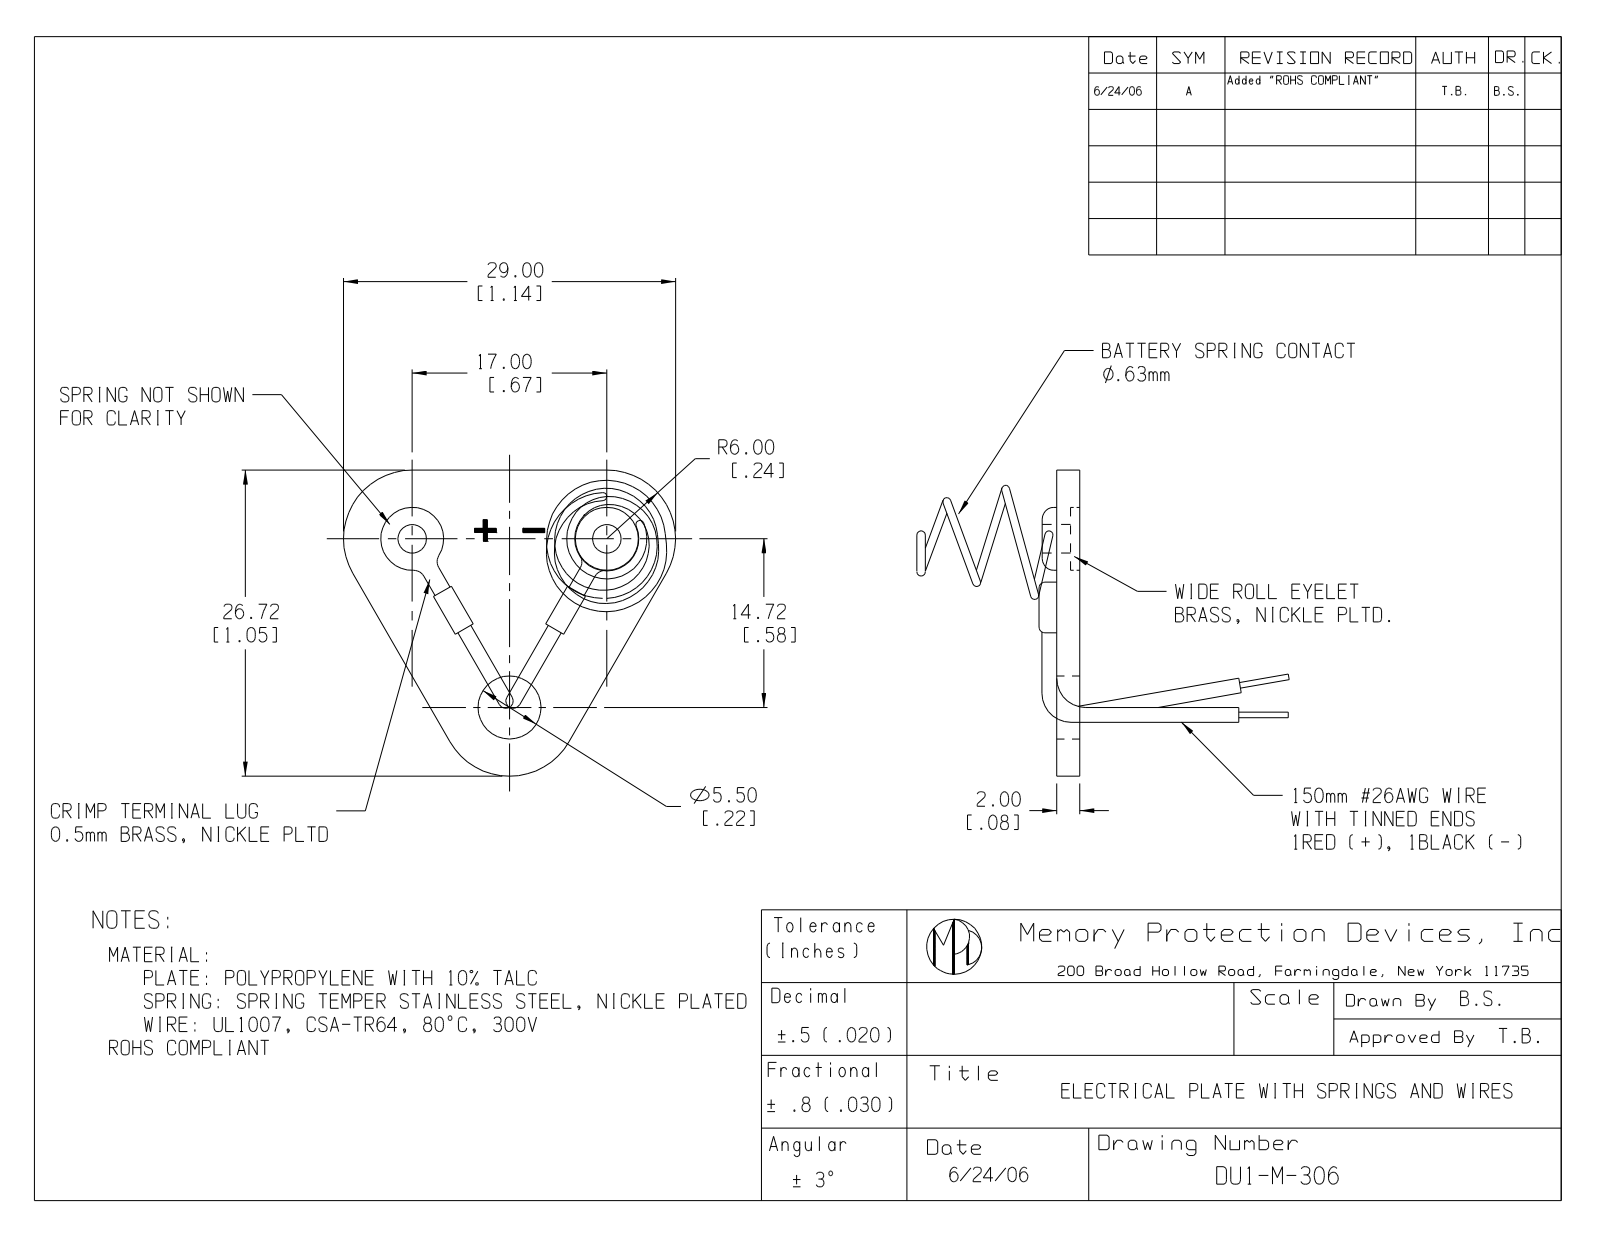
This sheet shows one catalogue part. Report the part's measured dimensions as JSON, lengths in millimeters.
{"part_name": "DU1-M-306", "step_written_by": "SolidWorks 2017 (AUTOMOTIVE_DESIGN)", "units": "millimeters", "bodies": {"solids": 7, "faces": 166, "planar": 57, "cylindrical": 69, "other": 40}, "overall_size": [156.5, 29, 26.72], "volume_mm3": 1523, "surface_area_mm2": 4062, "round_holes": [[0.48, 4], [5.5, 3], [2, 2], [3, 2]], "round_bosses_or_shafts": [[1.3, 4], [5, 2], [0.48, 2], [0.63, 1]], "partial_cylinders_radius": [[0.2, 4], [0.6, 4], [6, 3], [0.8, 2]], "face_to_face_distances": [2, 1.2, 0.8, 0.5, 1.5, 3.2, 2.7, 2.4, 1.7, 1.4], "hole_center_spacings": [17, 0.93, 16.3, 17.18, 1.74]}
